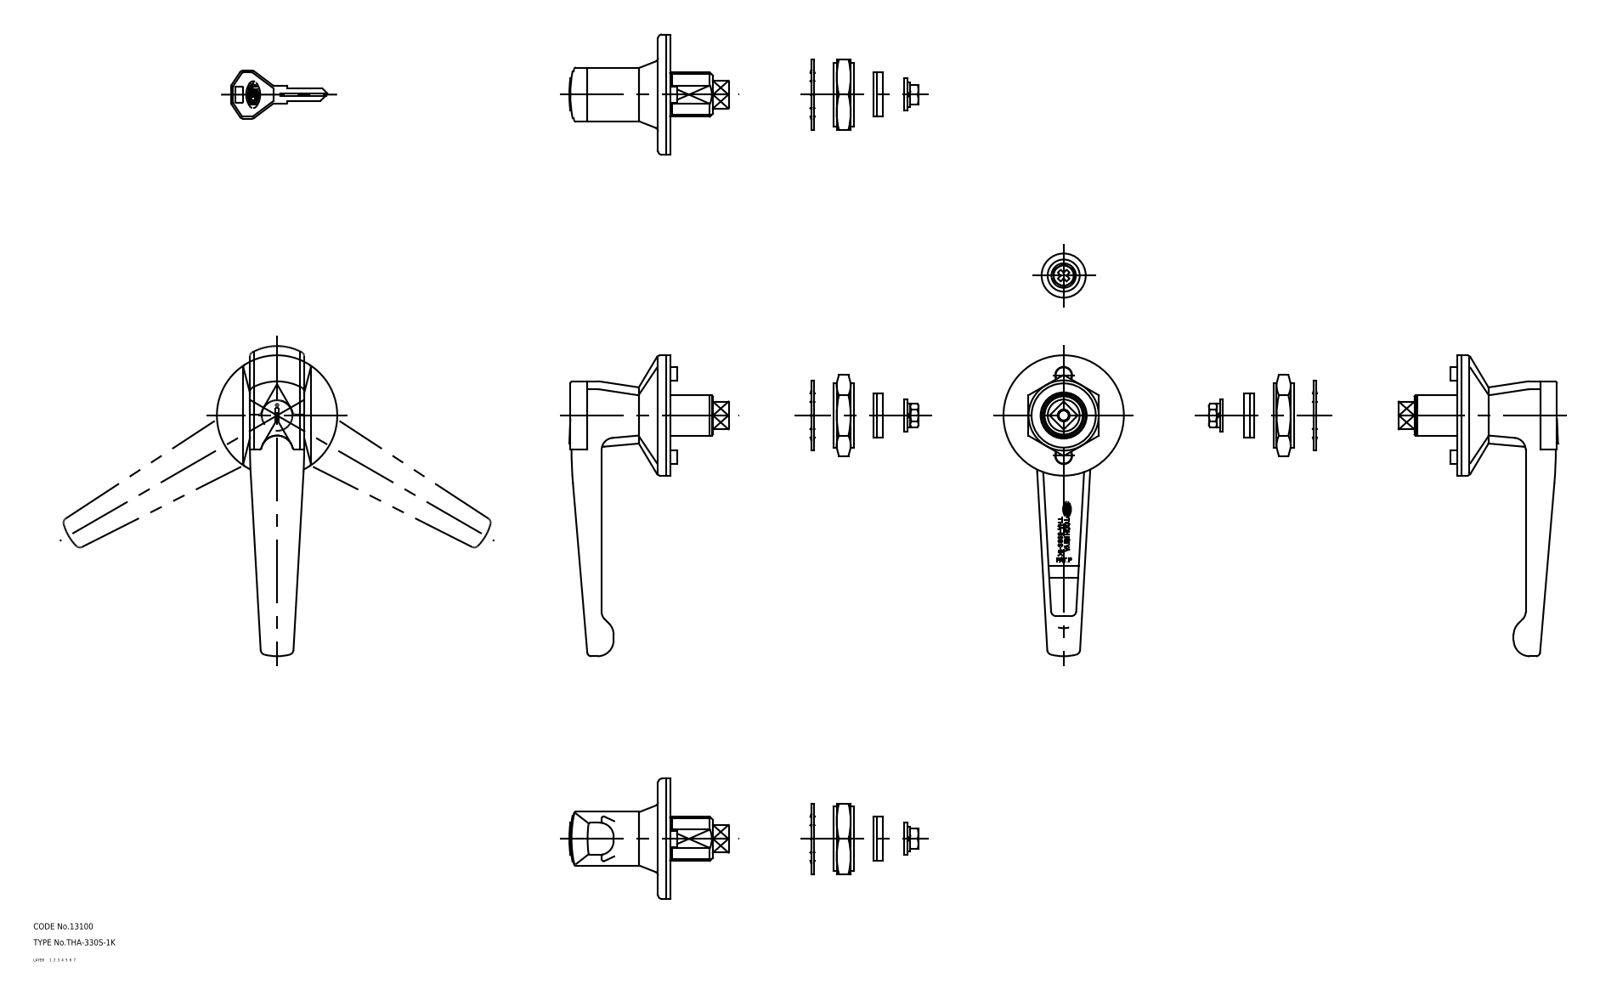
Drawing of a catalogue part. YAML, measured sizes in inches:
part_name: "washer_D; washer_C; washer_B; washer_A (+8 more)"
step_written_by: "CADfix (AUTOMOTIVE_DESIGN)"
units: inches
bodies: {solids: 11, faces: 349, planar: 0, cylindrical: 0, other: 349}
overall_size: [5.906, 5.86, 2.362]
volume: 5.367
surface_area: 64.85
